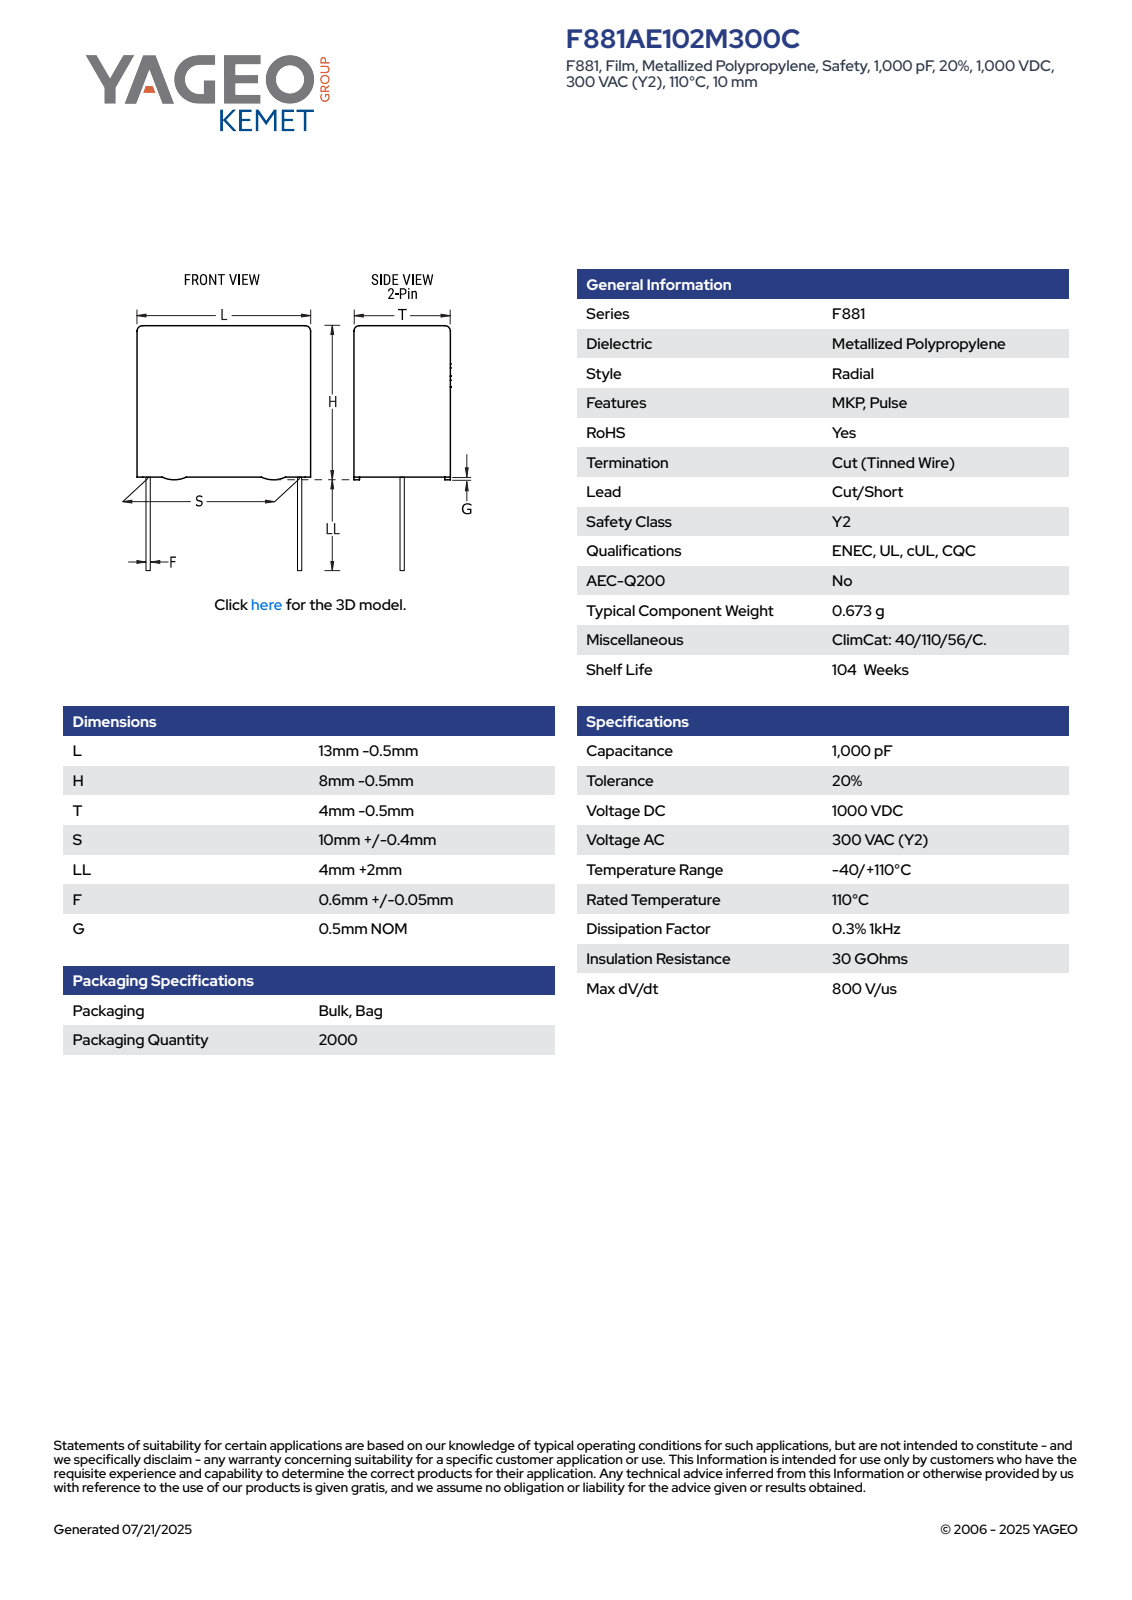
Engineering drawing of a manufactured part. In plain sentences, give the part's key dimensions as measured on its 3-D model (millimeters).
The part is named "CFR_RBG_13X8X4_L12.5H7.5T3.5S10LL6F0.65G0.5". Its 3-D file was written by "SolidWorks 2014 (AUTOMOTIVE_DESIGN)". It is 4 solids with 89 faces: 81 planar, 8 cylindrical and 0 other. Overall it measures 13.5 by 12.5 by 3.5 millimeters. Its volume is 310 cubic millimeters and its surface area 357 square millimeters. Round bosses or shafts: 2 of diameter 0.65. Partial cylindrical surfaces (rounded edges, fillets, slot ends): 4 of radius 0.5. The main face-to-face distances are 3.5, 7, 12.5, 3.3, 3.1, 0.5, 7.5, 6, 6.5, 13.5.
